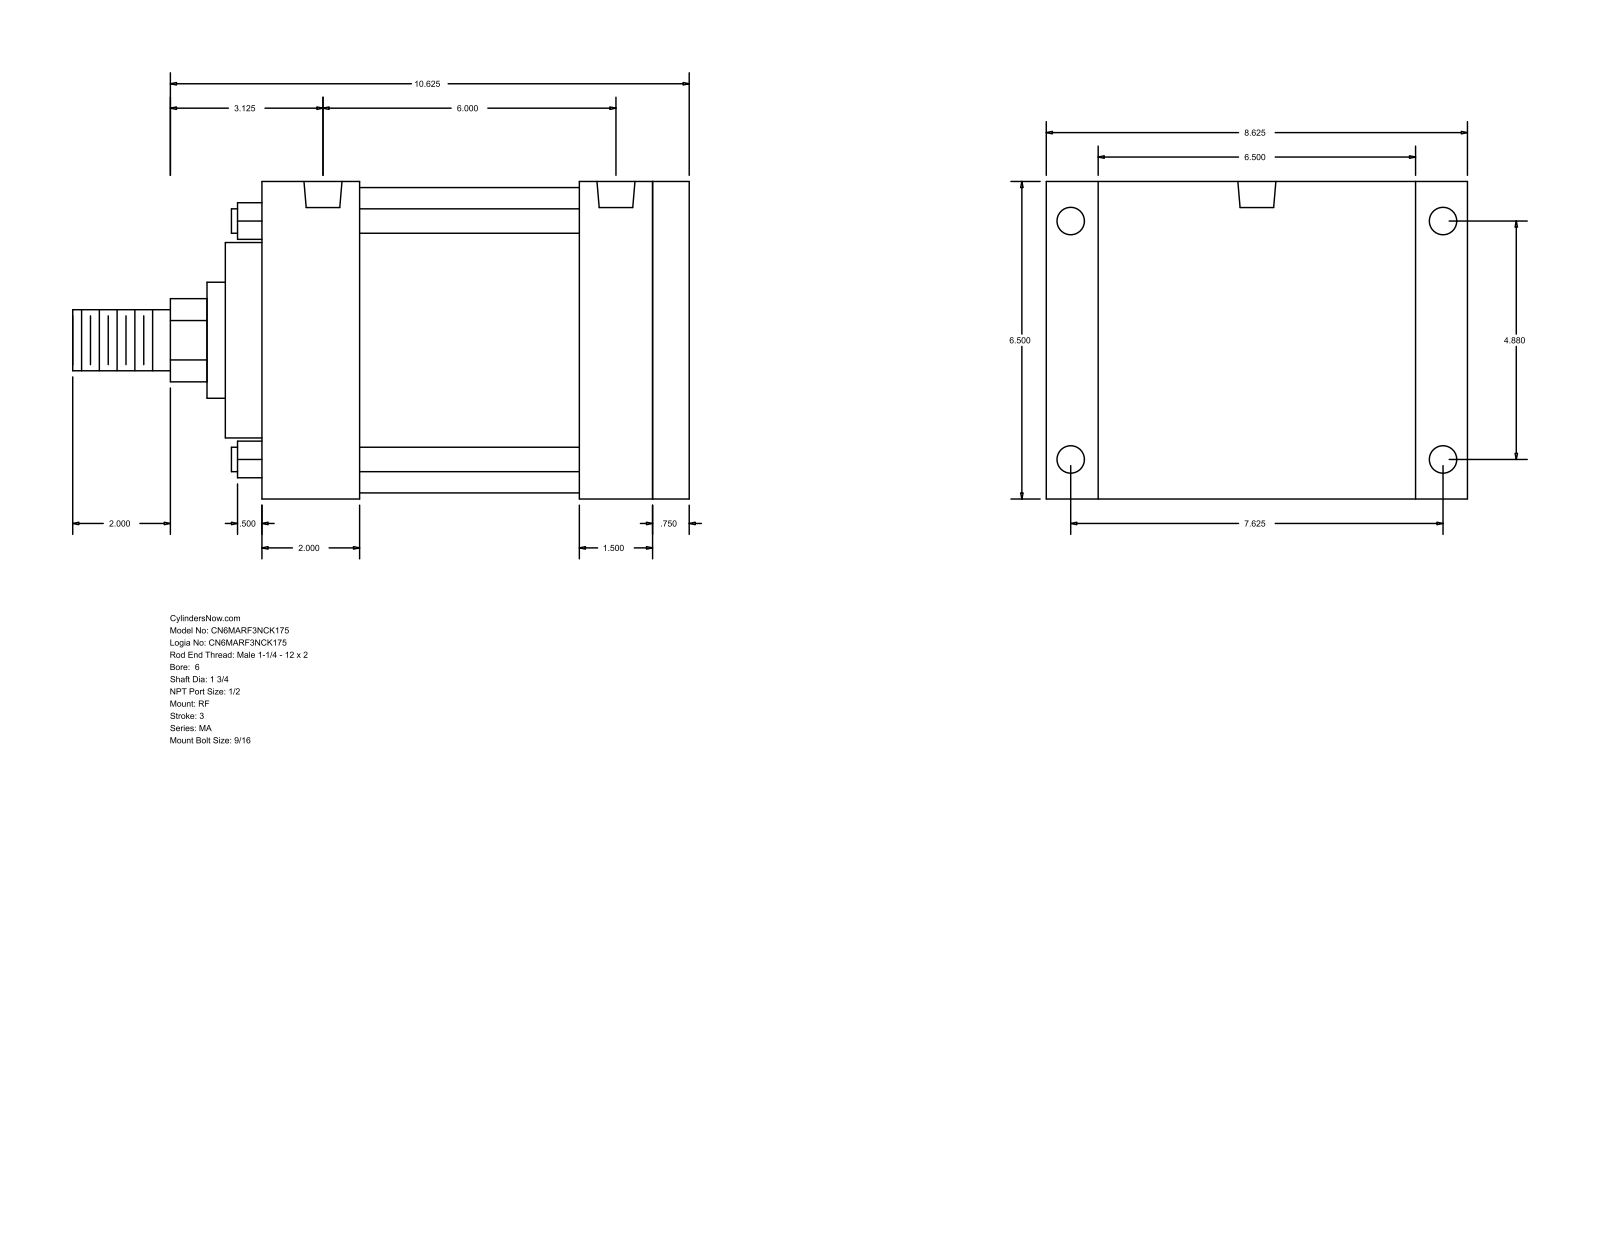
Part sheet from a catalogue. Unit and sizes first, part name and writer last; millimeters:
Units: millimetres
Overall size (bounding box): 320.68 × 219.07 × 165.1
Round holes (diameter × count): ⌀14.29 ×4, ⌀17.46 ×4, ⌀19.77 ×2
Round bosses / shafts (diameter × count): ⌀12.7 ×4, ⌀158.75 ×1, ⌀101.6 ×1, ⌀60.33 ×1, ⌀44.45 ×1, ⌀31.75 ×1
Partial cylindrical surfaces — rounded edges, fillets, slot ends (radius × count): R21.63 ×1
Main face-to-face distances: 165.1, 222.26, 203.2, 19.06, 38.1, 50.8, 19.05, 152.4, 171.46, 114.3
Hole centre spacings: 123.96, 152.4, 193.68, 229.95
Bodies: 0 solids, 94 faces (65 planar, 29 cylindrical, 0 other)
Part name (STEP PRODUCT): MA_RF__0600_1.75
STEP written by: GSSL Pune (CONFIG_CONTROL_DESIGN)
